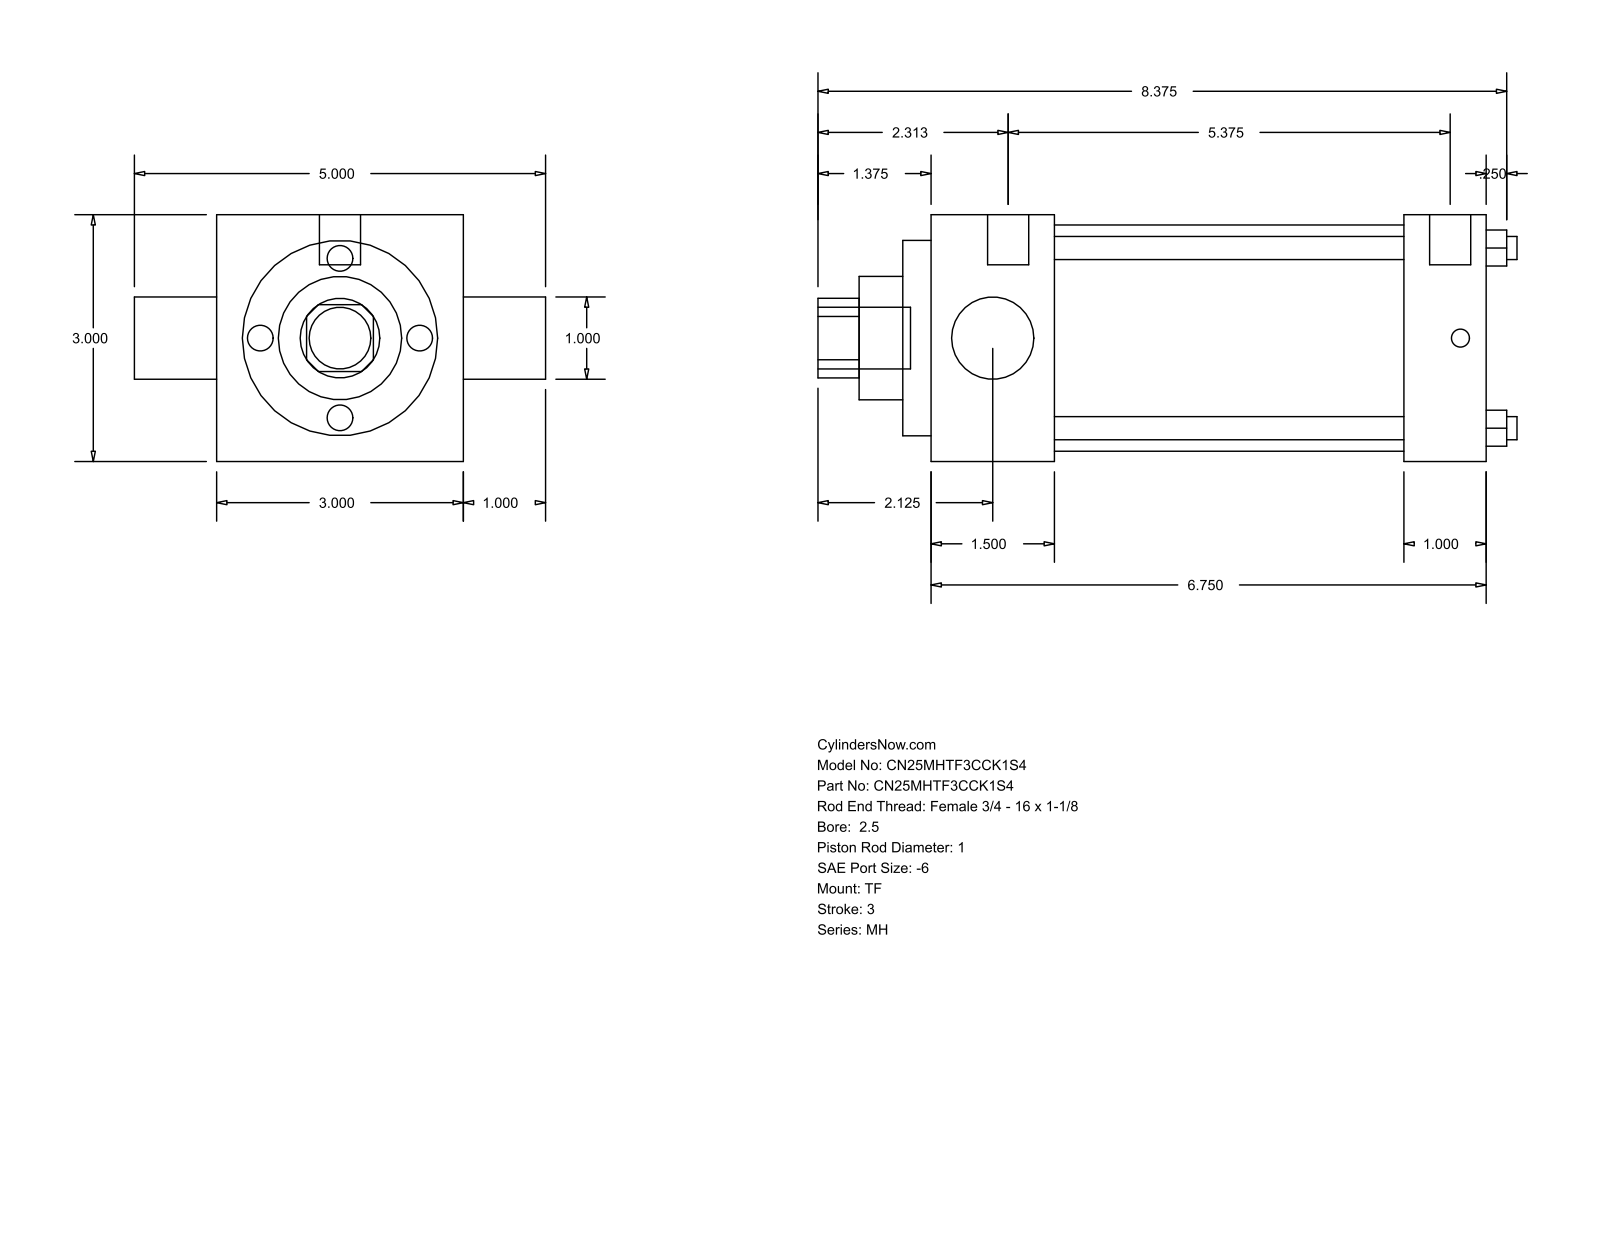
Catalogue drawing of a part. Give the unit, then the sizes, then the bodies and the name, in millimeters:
Units: millimetres
Overall size (bounding box): 215.9 × 127 × 76.2
Round holes (diameter × count): ⌀7.14 ×4, ⌀25.4 ×2, ⌀38.1 ×1, ⌀60.33 ×1, ⌀69.85 ×1
Round bosses / shafts (diameter × count): ⌀5.56 ×3, ⌀12.7 ×2, ⌀19.05 ×1
Partial cylindrical surfaces — rounded edges, fillets, slot ends (radius × count): R12.29 ×1
Main face-to-face distances: 76.2, 171.46, 38.11, 133.35, 146.05, 107.94, 25.41, 8.73, 46.84, 154.78
Hole centre spacings: 39.33, 55.62, 78.66
Bodies: 0 solids, 86 faces (61 planar, 25 cylindrical, 0 other)
Part name (STEP PRODUCT): MH_TF__0250_1
STEP written by: GSSL Pune (CONFIG_CONTROL_DESIGN)
